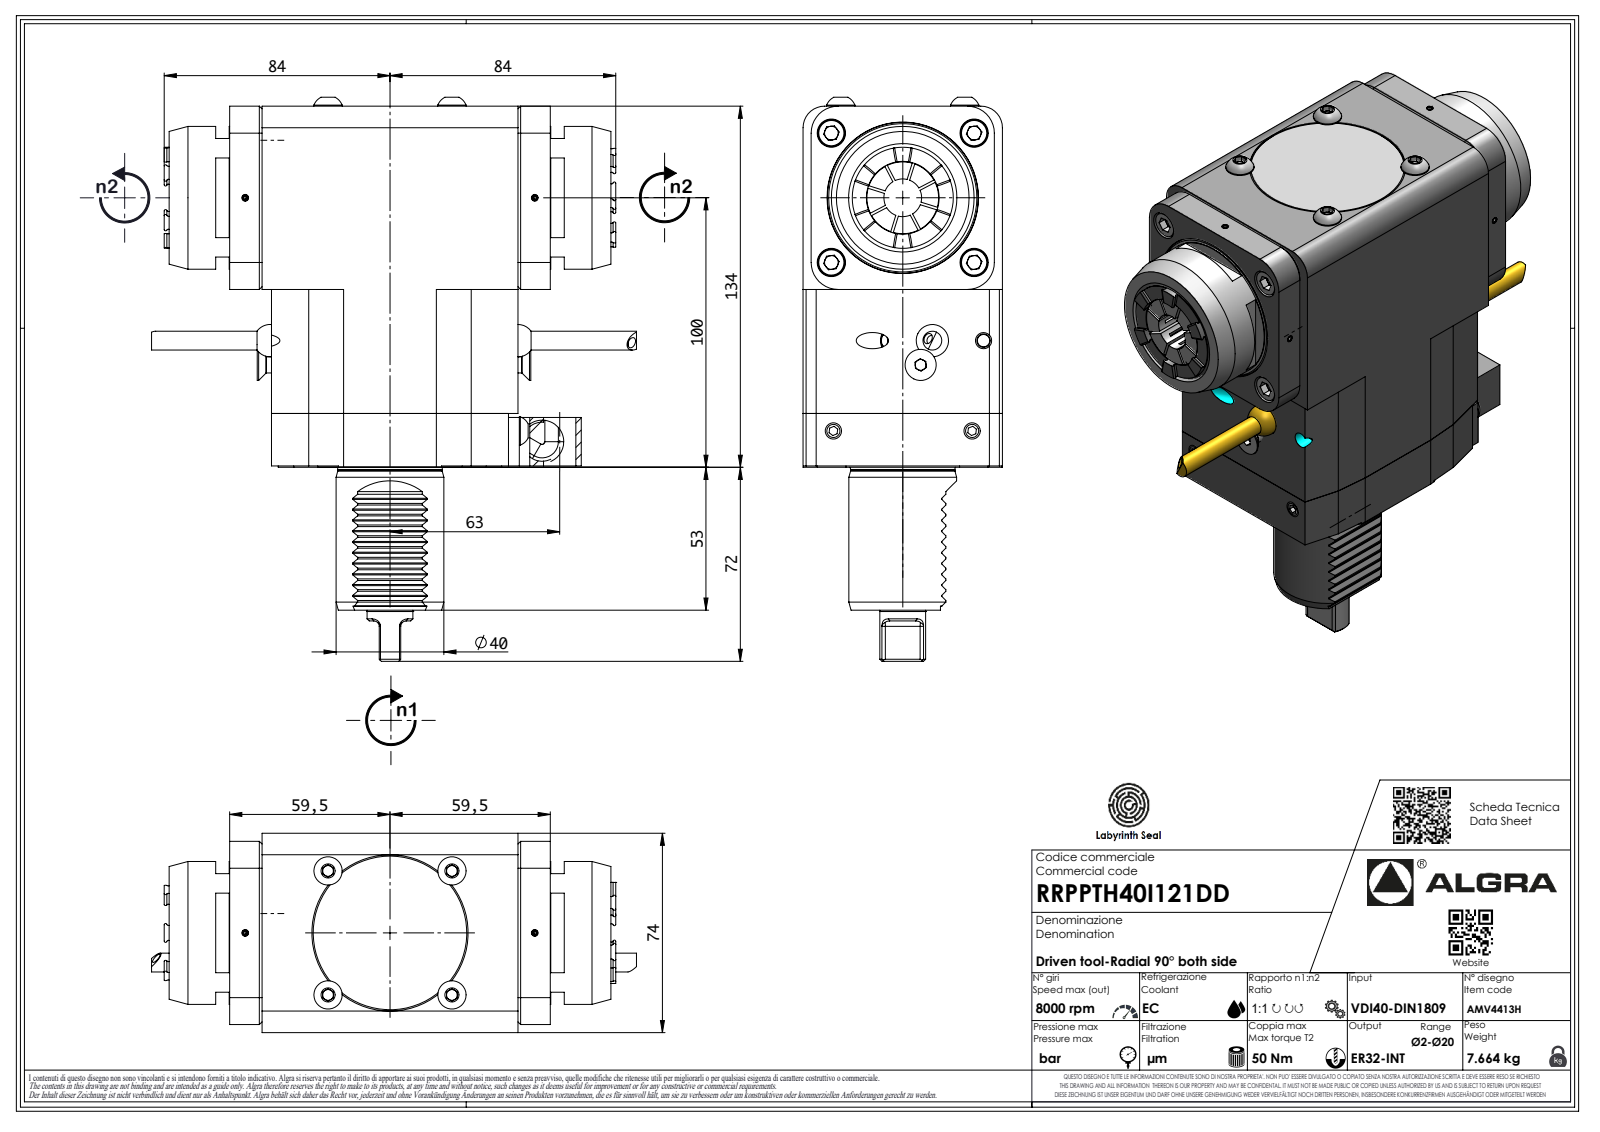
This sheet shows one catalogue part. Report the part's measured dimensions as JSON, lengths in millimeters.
{"part_name": "RRPPTH40I121DD", "step_written_by": "SolidWorks 2023 (AUTOMOTIVE_DESIGN)", "units": "millimeters", "bodies": {"solids": 1, "faces": 499, "planar": 347, "cylindrical": 72, "other": 80}, "overall_size": [206, 180, 74], "volume_mm3": 1193000, "surface_area_mm2": 85153, "round_holes": [[4, 2], [2.1, 1], [5, 1]], "round_bosses_or_shafts": [[53, 1], [40, 1], [38.7, 1], [17, 1], [16.98, 1], [7, 1], [6.37, 1], [1.7, 1]], "partial_cylinders_radius": [[0.3, 11], [0.33, 7], [0.52, 7], [2, 7], [3.7, 7], [10, 4], [8, 2], [0.21, 1]], "face_to_face_distances": [74, 12, 22.5, 141.5, 134, 119, 91.5, 68, 107, 103.5], "hole_center_spacings": [122.3]}
